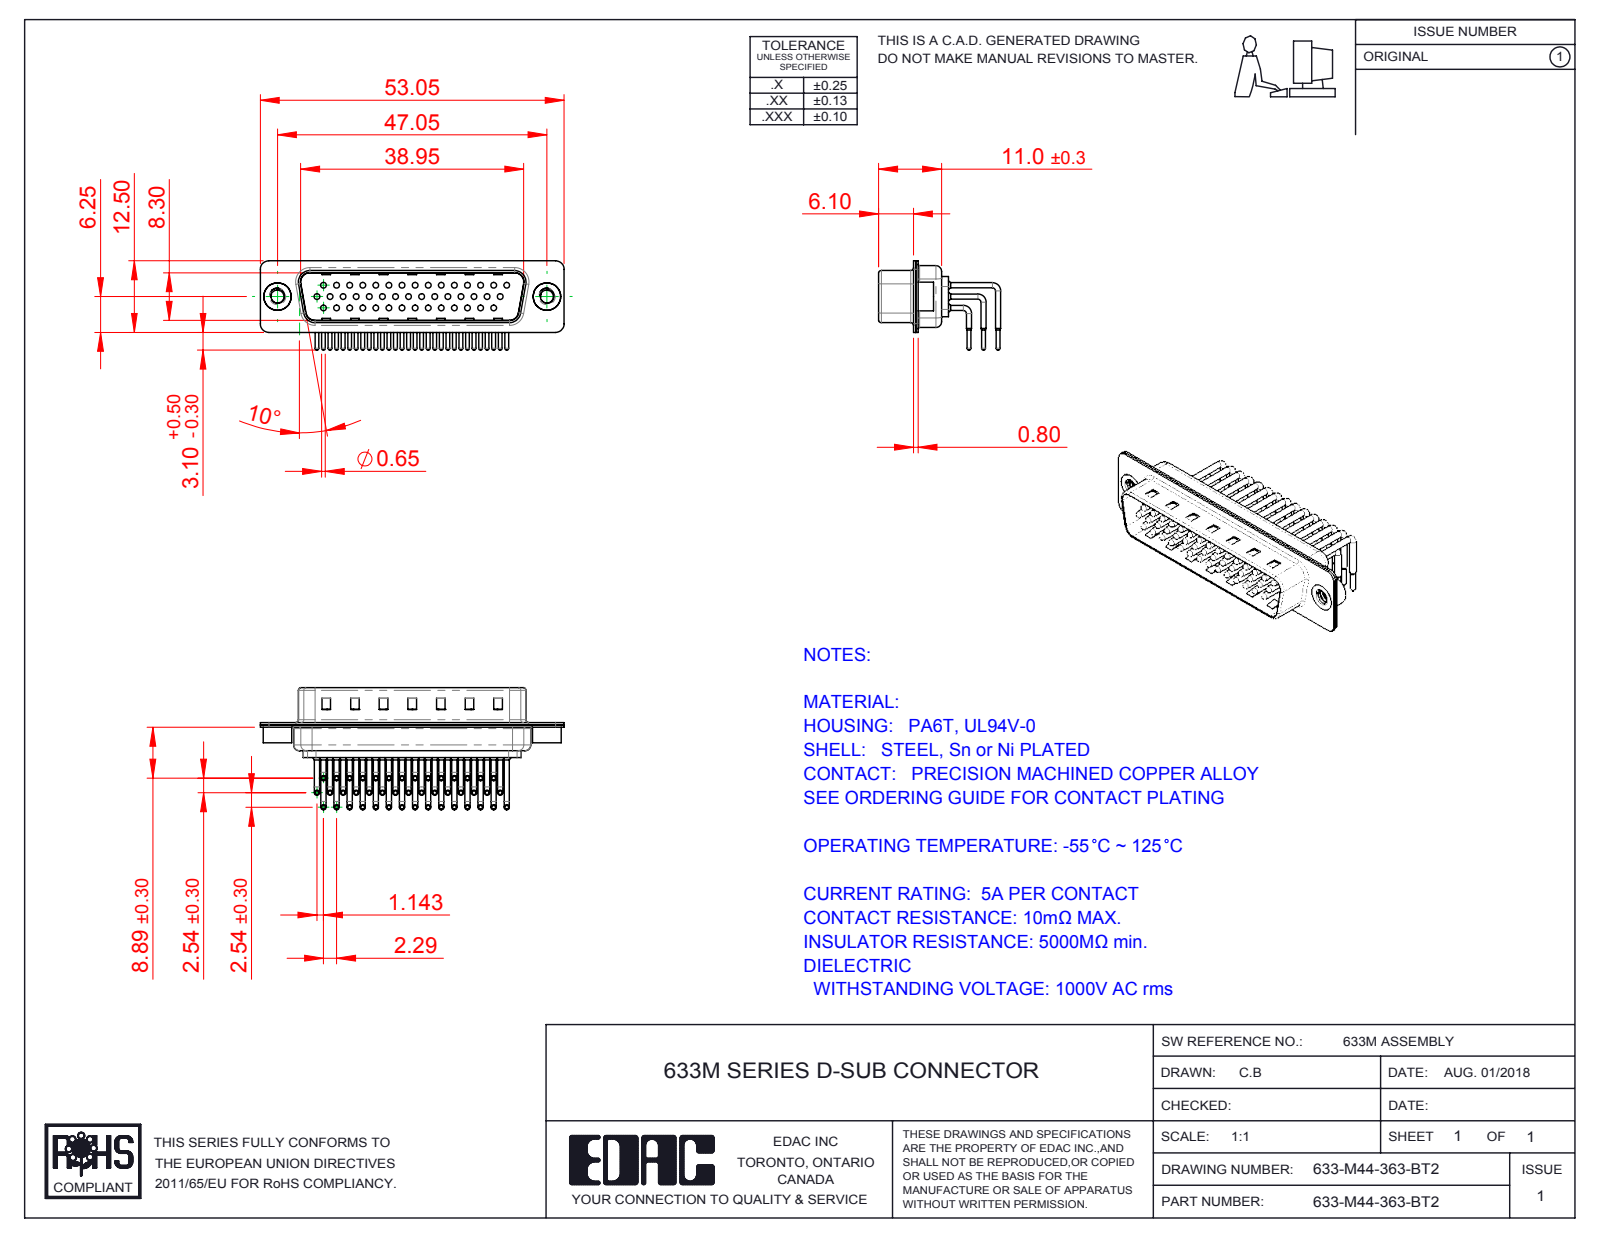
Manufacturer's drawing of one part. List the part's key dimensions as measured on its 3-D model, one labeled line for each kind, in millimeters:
Part name (STEP PRODUCT): 633M Shell Front_44 Contacts; 633M Housing_44 Contacts; 633-M44-363-BT2; 633M 4-40 Threaded Rivet (+4 more)
STEP written by: SolidWorks 2016 (CONFIG_CONTROL_DESIGN)
Units: millimetres
Bodies: 49 solids, 5216 faces (2987 planar, 1721 cylindrical, 508 other)
Overall size (bounding box): 53.05 × 21.32 × 15.6
Volume: 3 136 mm³ · Surface area: 10 056 mm²
Round holes (diameter × count): ⌀1 ×44, ⌀1.7 ×44, ⌀2 ×44, ⌀2.26 ×2, ⌀4 ×2, ⌀4.8 ×2
Round bosses / shafts (diameter × count): ⌀0.9 ×88, ⌀1.5 ×44, ⌀0.65 ×44, ⌀5 ×2, ⌀4.9 ×2, ⌀1 ×2
Partial cylindrical surfaces — rounded edges, fillets, slot ends (radius × count): R1.01 ×44, R1.5 ×16, R2 ×12, R0.5 ×8, R1.6 ×8, R0.25 ×4, R0.6 ×4, R0.65 ×4
Main face-to-face distances: 0.4, 0.85, 9.55, 1.5, 8.7, 1.9, 1.25, 10.4, 0.35, 9.15
Hole centre spacings: 2.28, 3.96, 2.29, 4.57, 8.24, 6.86, 11.43, 12.72
